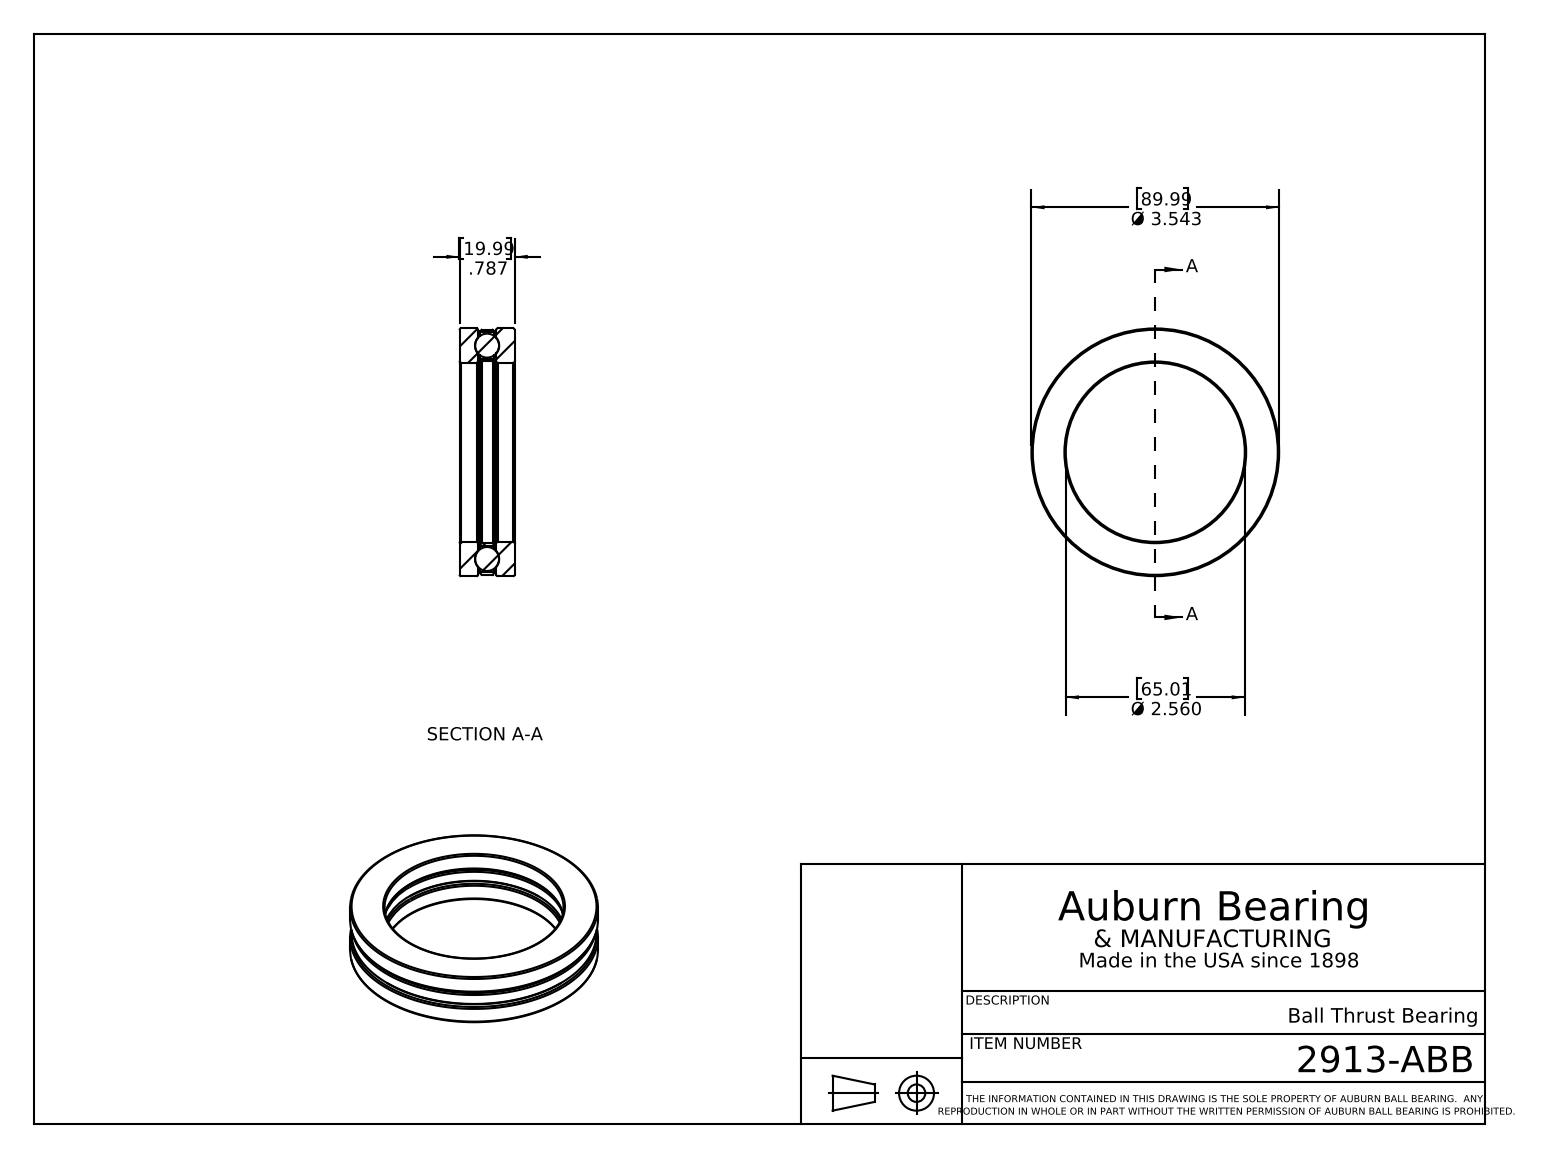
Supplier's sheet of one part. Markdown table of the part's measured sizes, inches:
| quantity | value |
| --- | --- |
| part name | 2913-ABB |
| STEP written by | SolidWorks 2018 (CONFIG_CONTROL_DESIGN) |
| units | inches |
| bodies | 7 solids, 64 faces (8 planar, 20 cylindrical, 36 other) |
| overall size | 3.543 × 3.543 × 0.787 |
| volume | 3.182 in³ |
| surface area | 42.12 in² |
| round holes (diameter × count) | 0.385 × 4, 2.56 × 1, 2.6 × 1 |
| round bosses / shafts (diameter × count) | 3.543 × 1, 3.503 × 1 |
| main face-to-face distances | 0.295, 0.492, 0.262, 0.524, 0.033, 0.23, 0.787, 0.197 |
| hole center spacings | 1.526, 2.157, 3.051 |
